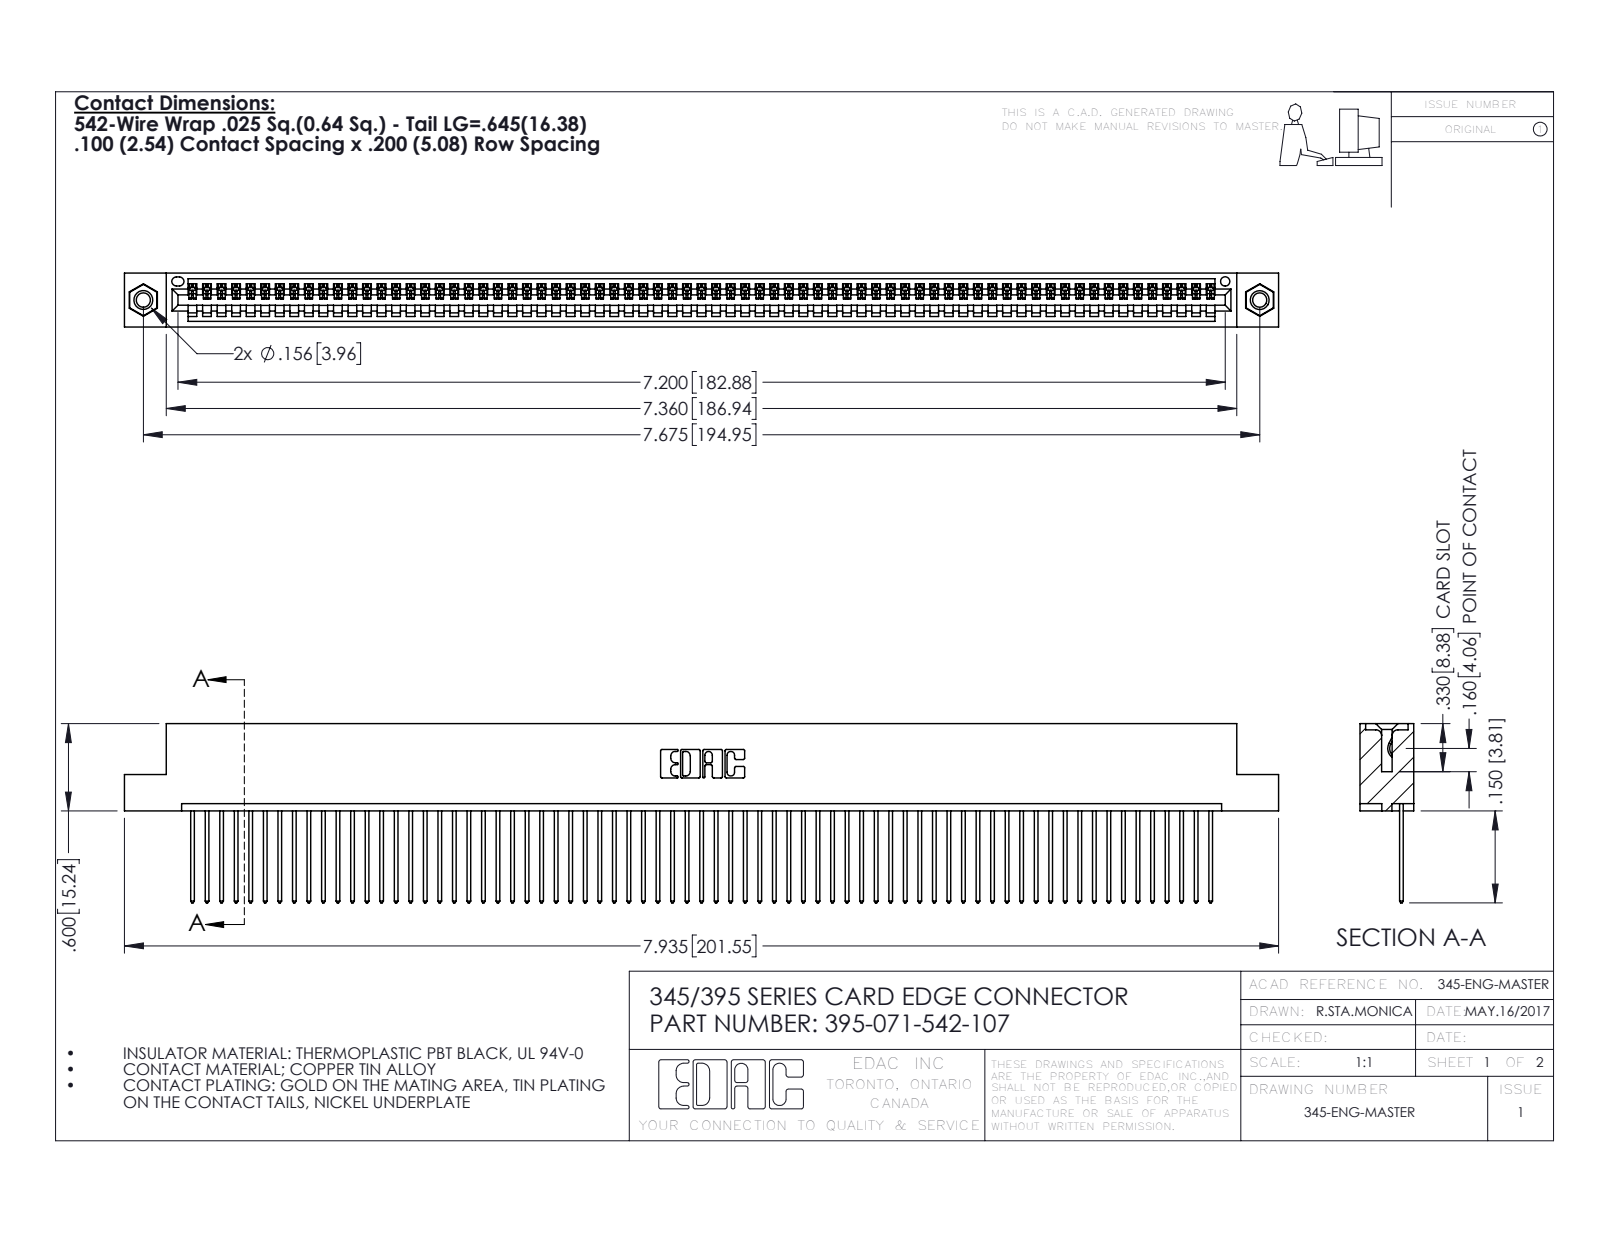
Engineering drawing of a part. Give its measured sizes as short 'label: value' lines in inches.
name: 345-250-001_345-250-005-103; 345 Part_Flush Mounting Lugs - 0.156 Dia-TI; 395-071-542-107; 345-292-001_345-293-142
written by: SolidWorks 2016 (CONFIG_CONTROL_DESIGN)
unit: in
bodies: 74 solids, 4304 faces (2952 planar, 1336 cylindrical, 16 other)
size: 7.935 × 1.232 × 0.37
volume: 1.192 in³; area: 42.43 in²
holes: 2× ⌀0.098, 2× ⌀0.125, 2× ⌀0.156, 1× ⌀0.064
bosses: 2× ⌀0.155
rounds: 142× R0.006, 142× R0.01, 22× R0.01, 6× R0.007, 6× R0.031, 3× R0.026, 2× R0.031, 2× R0.04
face distances: 0.072, 0.298, 0.098, 0.272, 0.025, 0.37, 0.2, 0.225, 0.149, 0.072
hole spacings: 0.27, 7.439, 7.675
